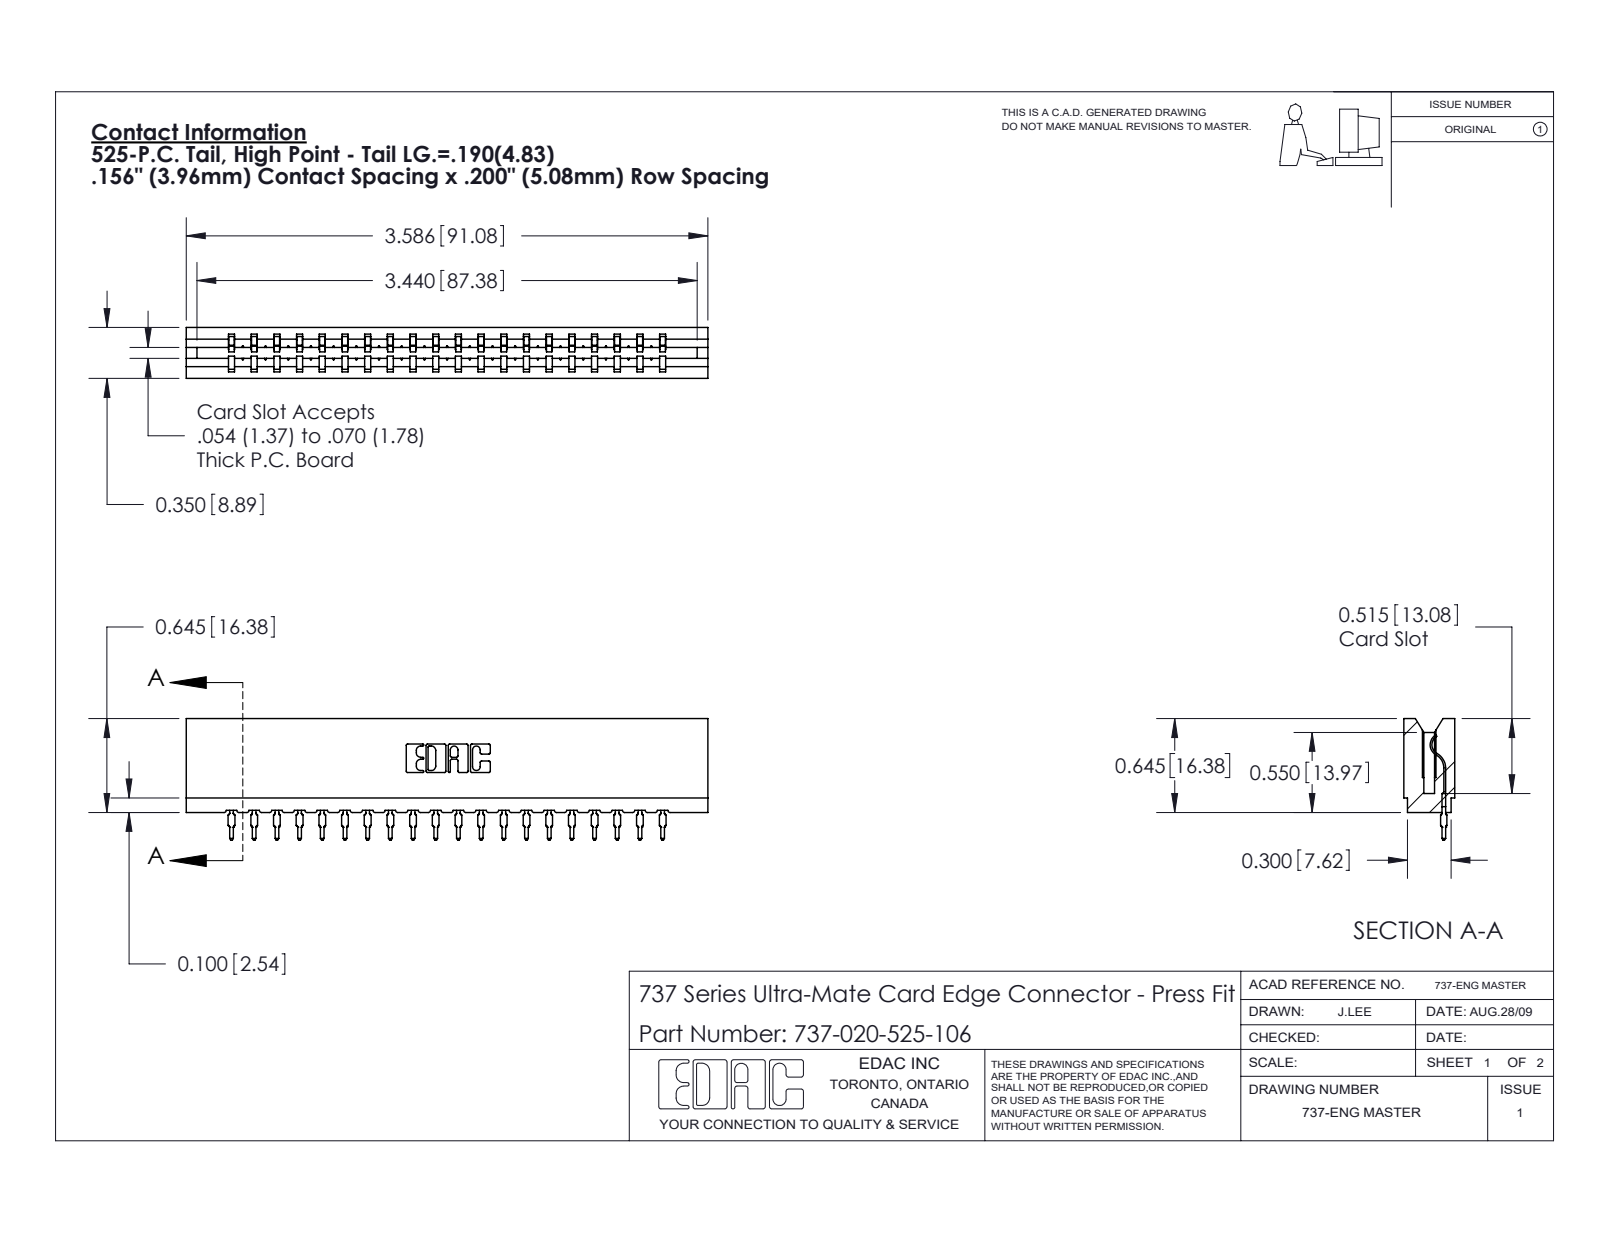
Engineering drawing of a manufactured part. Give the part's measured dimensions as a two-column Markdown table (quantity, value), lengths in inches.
| quantity | value |
| --- | --- |
| part name | 745-292-001_525; 737-020-525-106; 737 Part_Insulator Option - 06 |
| STEP written by | SolidWorks 2020 (CONFIG_CONTROL_DESIGN) |
| units | inches |
| bodies | 21 solids, 2355 faces (1415 planar, 420 cylindrical, 520 other) |
| overall size | 3.586 × 0.836 × 0.35 |
| volume | 0.544 in³ |
| surface area | 17.87 in² |
| partial cylindrical surfaces (radius × count) | 0.015 × 40, 0.021 × 40, 0.01 × 22, 0.007 × 6, 0.031 × 6, 0.005 × 4, 0.011 × 4, 0.026 × 3 |
| main face-to-face distances | 0.138, 0.212, 0.35, 0.156, 0.624, 0.468, 0.78, 0.074, 0.045, 0.305 |
